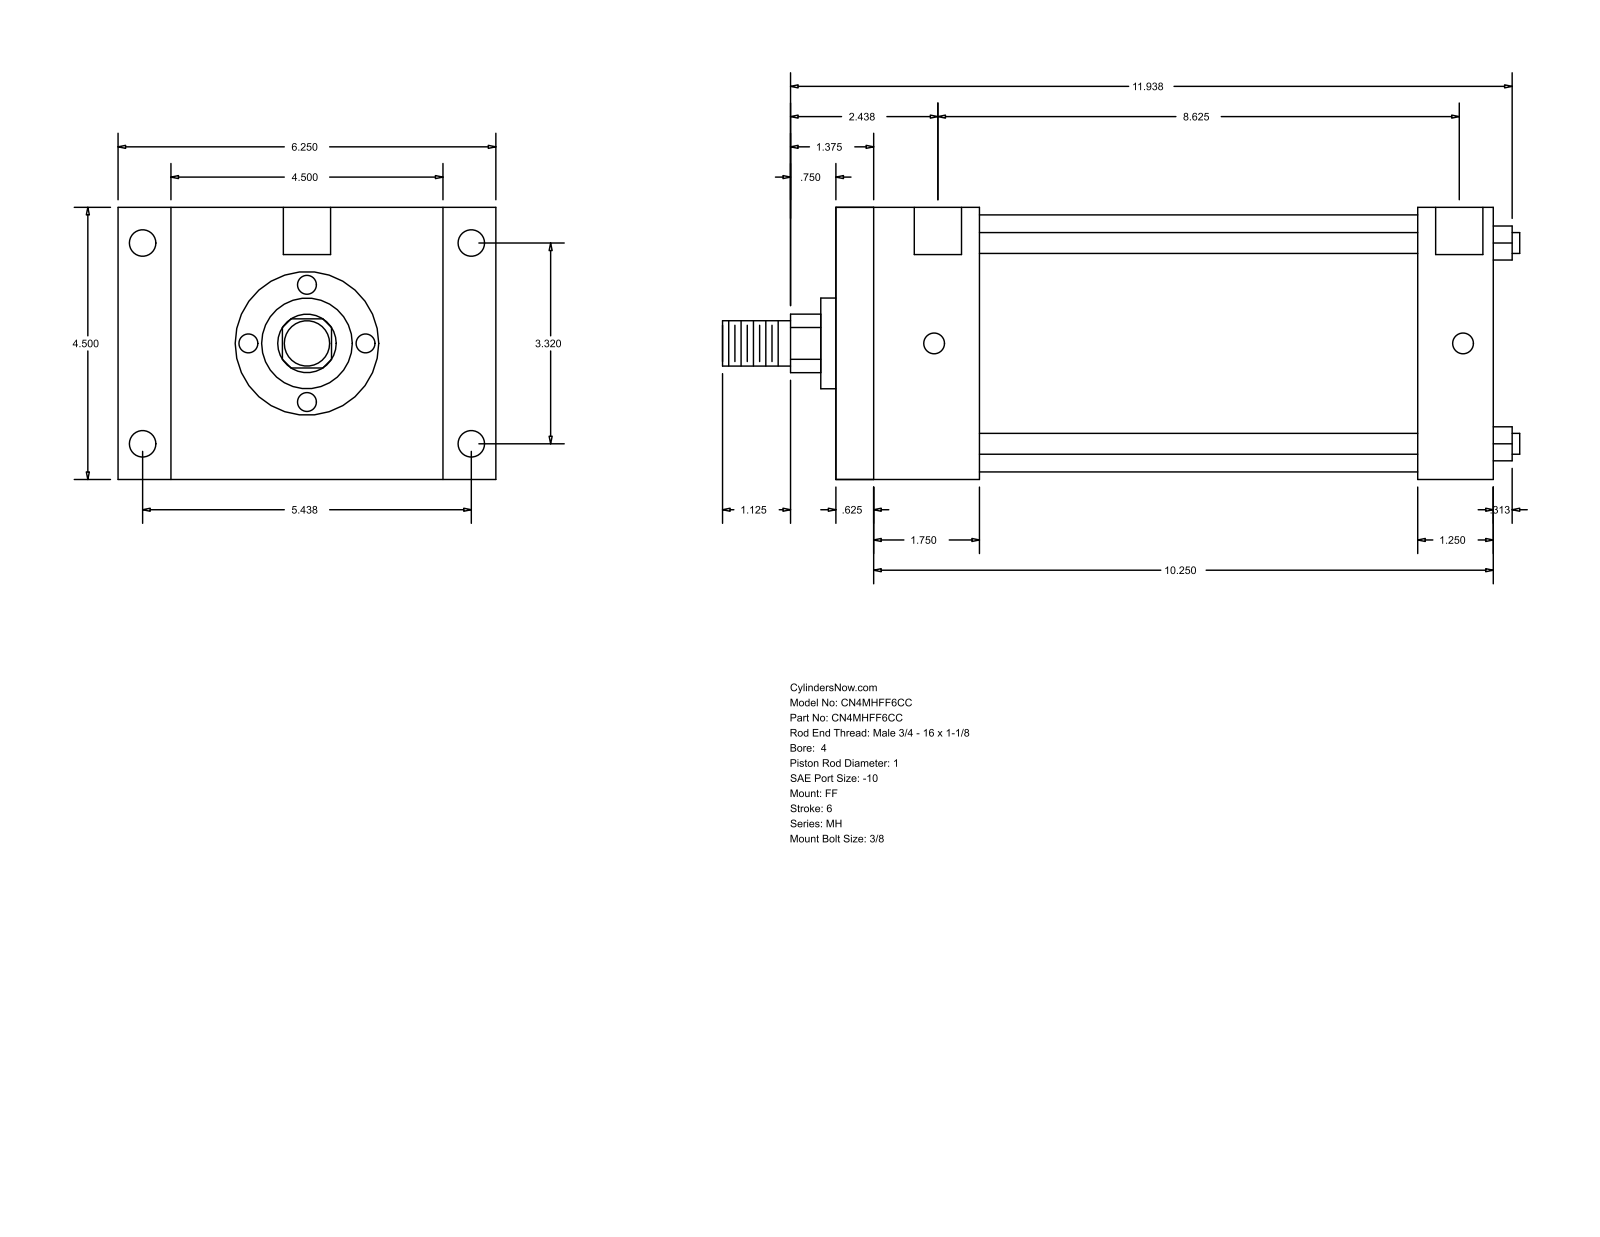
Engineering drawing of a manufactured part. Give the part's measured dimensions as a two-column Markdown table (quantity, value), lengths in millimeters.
| quantity | value |
| --- | --- |
| part name | MH_FF__0400_1 |
| STEP written by | GSSL Pune (CONFIG_CONTROL_DESIGN) |
| units | millimeters |
| bodies | 0 solids, 92 faces (64 planar, 28 cylindrical, 0 other) |
| overall size | 334.96 × 158.75 × 114.3 |
| round holes (diameter × count) | 8.73 × 4, 11.13 × 4, 19.84 × 2 |
| round bosses / shafts (diameter × count) | 8.76 × 4, 107.95 × 1, 38.1 × 1, 25.4 × 1, 19.05 × 1 |
| partial cylindrical surfaces (radius × count) | 12.29 × 1 |
| main face-to-face distances | 114.3, 276.22, 15.87, 260.35, 60.33, 44.46, 215.89, 244.47, 228.6, 184.14 |
| hole center spacings | 1.58, 84.32, 138.12, 161.82, 220.66, 222.24, 219.08 |
